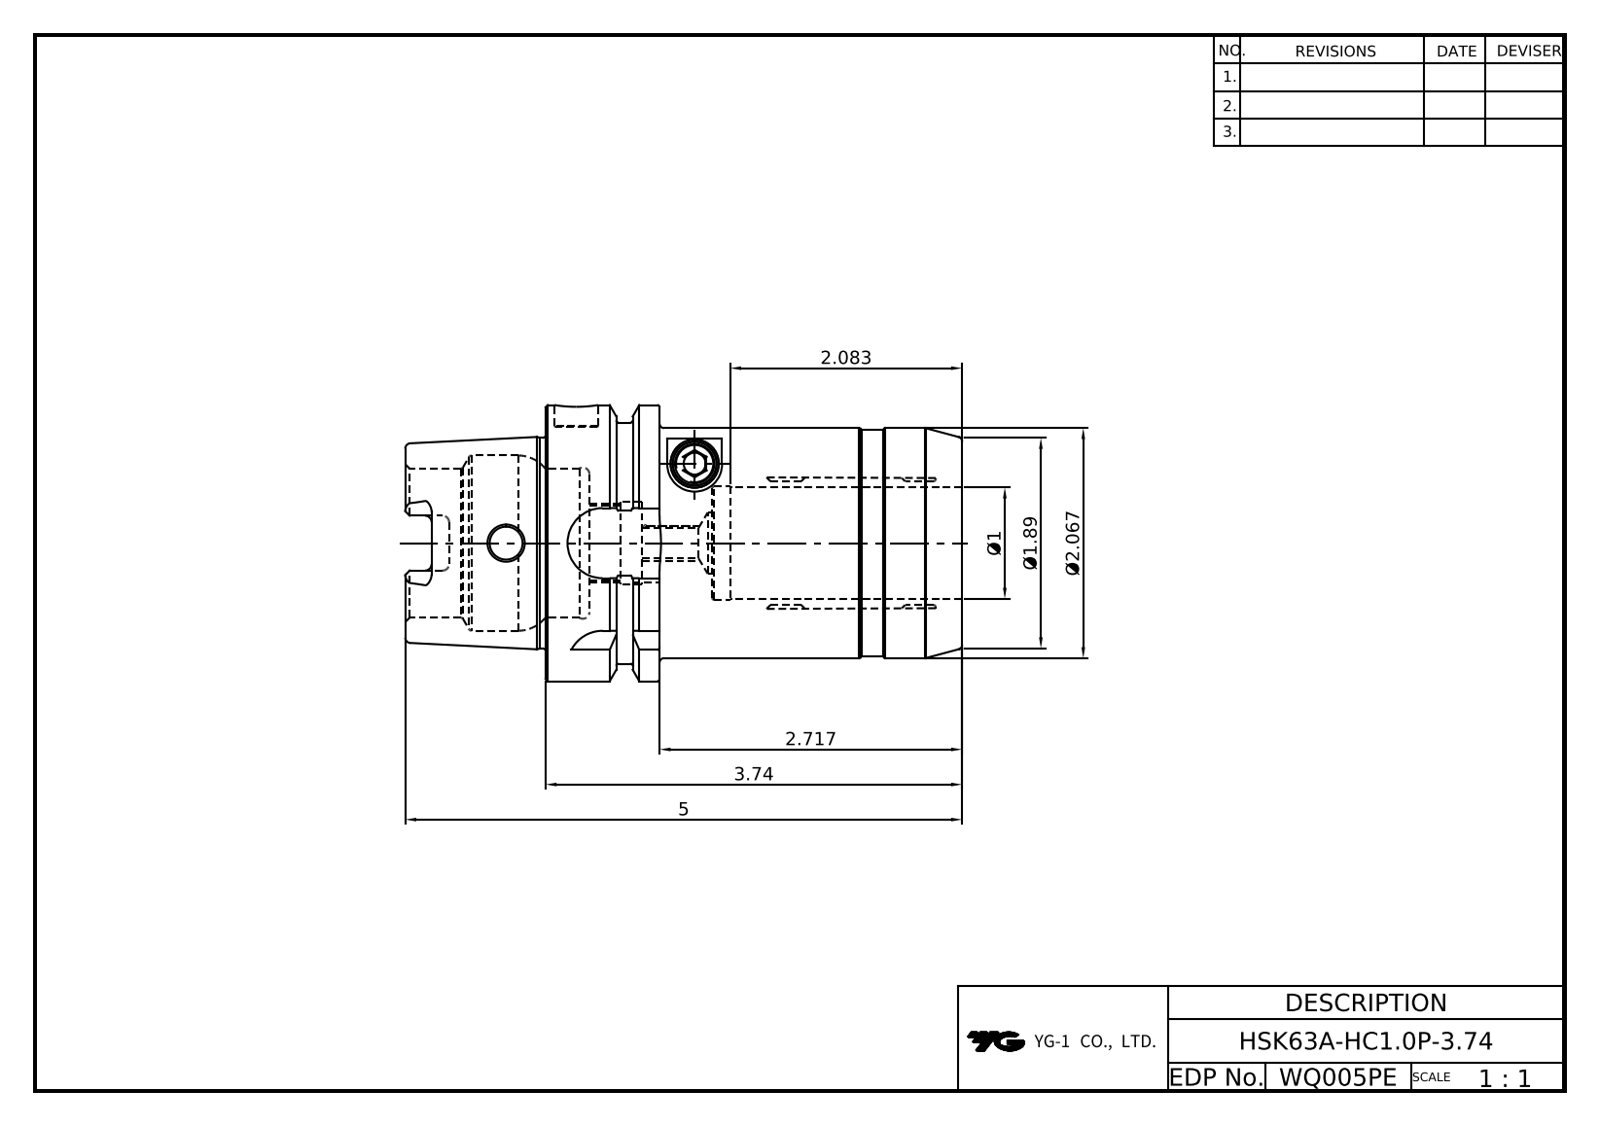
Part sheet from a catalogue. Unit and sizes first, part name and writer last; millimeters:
Units: millimetres
Overall size (bounding box): 127 × 63 × 63
Round holes (diameter × count): ⌀6.92 ×1, ⌀7.5 ×1, ⌀10 ×1, ⌀14 ×1, ⌀16.92 ×1, ⌀19 ×1, ⌀25.4 ×1, ⌀26.2 ×1, ⌀34 ×1, ⌀40 ×1
Round bosses / shafts (diameter × count): ⌀63 ×1, ⌀55 ×1, ⌀52.5 ×1, ⌀51.5 ×1, ⌀48.04 ×1
Partial cylindrical surfaces — rounded edges, fillets, slot ends (radius × count): R1.5 ×6, R2.88 ×4, R8 ×4
Main face-to-face distances: 95, 16, 12, 10, 26, 85, 69, 32, 28, 38
Volume: 199 282 mm³ · Surface area: 38 140 mm²
Bodies: 1 solid, 126 faces (43 planar, 36 cylindrical, 47 other)
Part name (STEP PRODUCT): LO-HSK63A-HC25.4P-95
STEP written by: Autodesk Inventor 2022 (AUTOMOTIVE_DESIGN)
